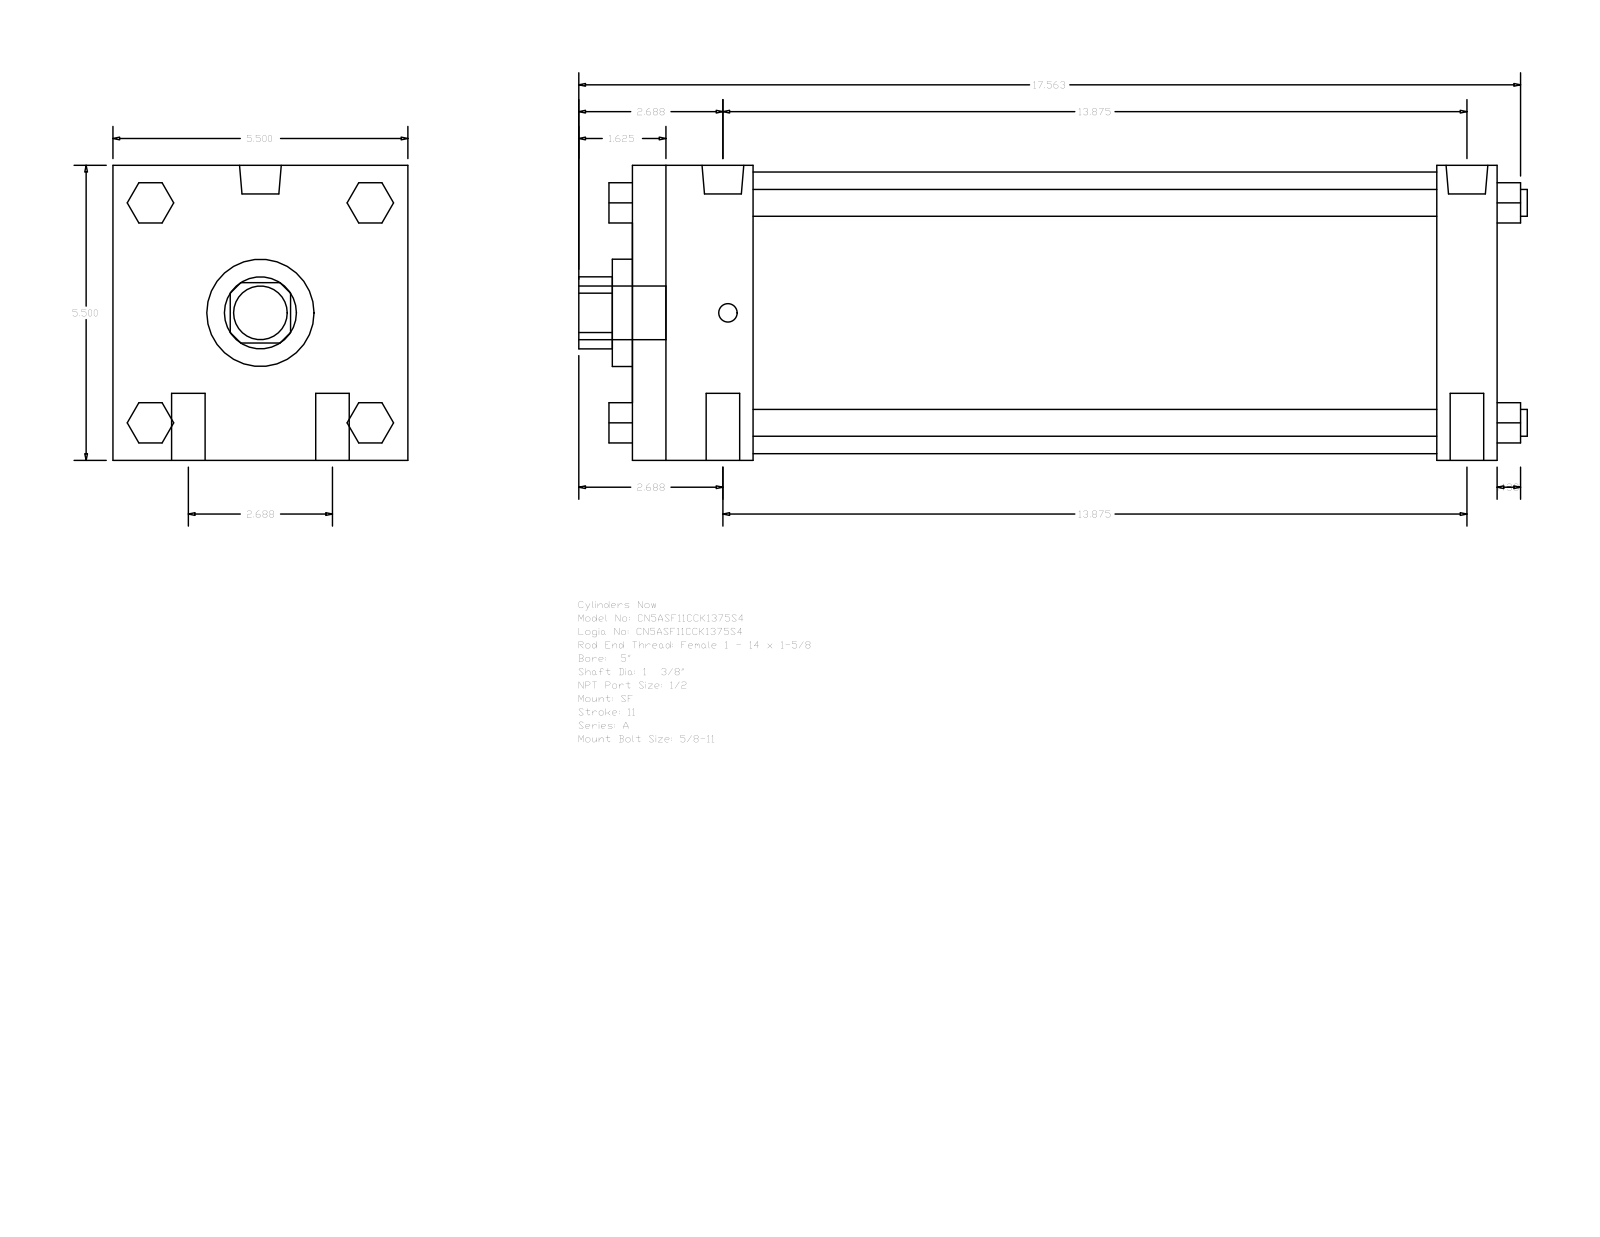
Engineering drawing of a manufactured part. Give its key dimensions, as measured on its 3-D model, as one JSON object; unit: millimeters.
{"part_name": "A_SF__0500_1.375", "step_written_by": "GSSL Pune (CONFIG_CONTROL_DESIGN)", "units": "millimeters", "bodies": {"solids": 0, "faces": 124, "planar": 94, "cylindrical": 30, "other": 0}, "overall_size": [449.26, 139.7, 139.7], "round_holes": [[34.92, 1], [50.8, 1], [133.35, 1]], "round_bosses_or_shafts": [[15.88, 4], [12.7, 4], [19.77, 2], [8.73, 2], [25.4, 1]], "partial_cylinders_radius": [[17.06, 1]], "face_to_face_distances": [139.7, 409.58, 28.58, 57.15, 381, 323.85, 352.43, 19.05, 52.07, 90.18]}
